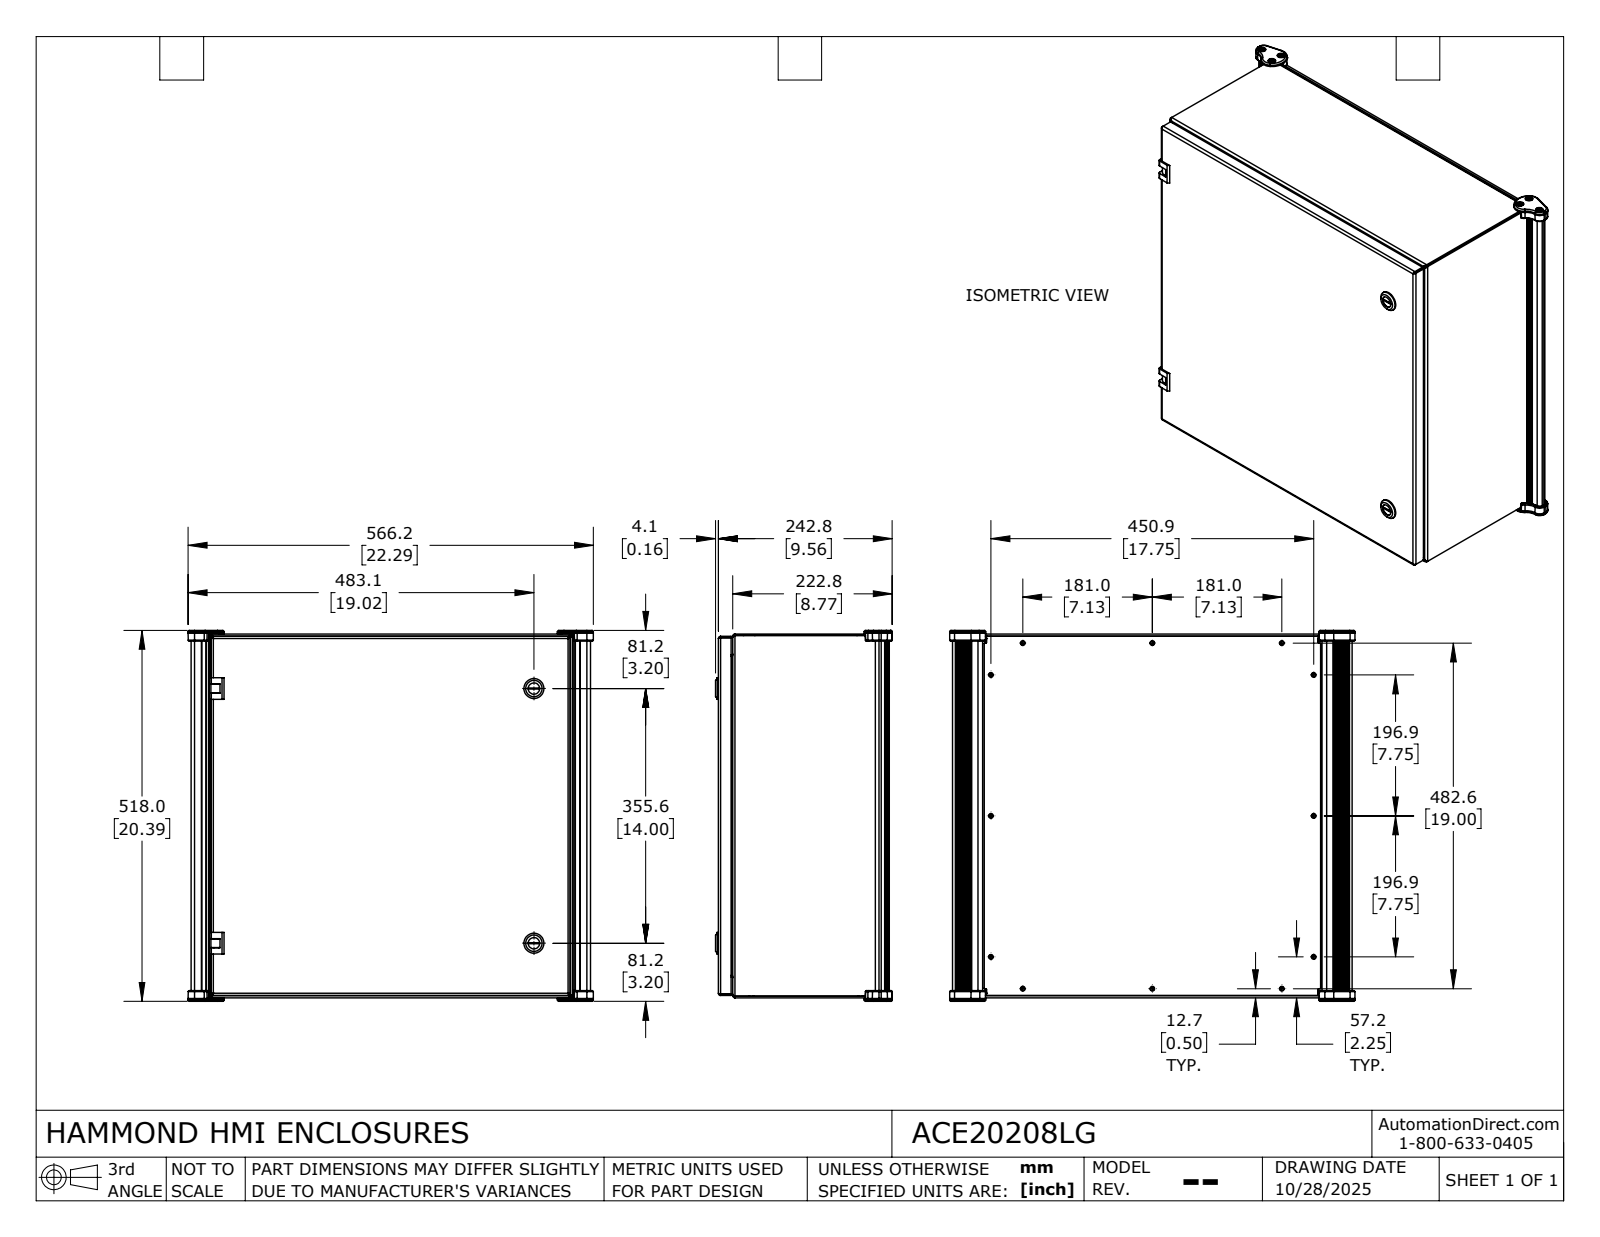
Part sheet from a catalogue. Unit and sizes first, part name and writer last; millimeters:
Units: millimetres
Overall size (bounding box): 566.22 × 518.03 × 246.86
Round holes (diameter × count): ⌀3.97 ×14, ⌀5.94 ×14, ⌀4.83 ×12, ⌀5.2 ×6, ⌀10.5 ×6, ⌀4.98 ×5, ⌀4.04 ×4, ⌀10.32 ×4, ⌀4.06 ×2, ⌀5 ×2, ⌀5.89 ×2, ⌀6.35 ×2
Round bosses / shafts (diameter × count): ⌀6.5 ×12, ⌀6.35 ×6, ⌀4.83 ×6, ⌀3.79 ×6, ⌀5.99 ×5, ⌀9.53 ×4, ⌀8.38 ×4, ⌀27.94 ×2
Partial cylindrical surfaces — rounded edges, fillets, slot ends (radius × count): R0.25 ×38, R1.5 ×30, R1.03 ×20, R3.09 ×20, R0.4 ×16, R0.75 ×16, R1.27 ×16, R1 ×14
Main face-to-face distances: 2.06, 505.94, 224.3, 3.18, 226.36, 227.48, 229.54, 3.17, 503.88, 508
Hole centre spacings: 152.4, 355.6, 62.86, 178.69, 180.97, 196.85, 229.76, 233.46
Volume: 3 200 000 mm³ · Surface area: 2 791 000 mm²
Bodies: 99 solids, 2540 faces (1210 planar, 865 cylindrical, 465 other)
Part name (STEP PRODUCT): ACE20208LG
STEP written by: SolidWorks 2024 (AUTOMOTIVE_DESIGN)
